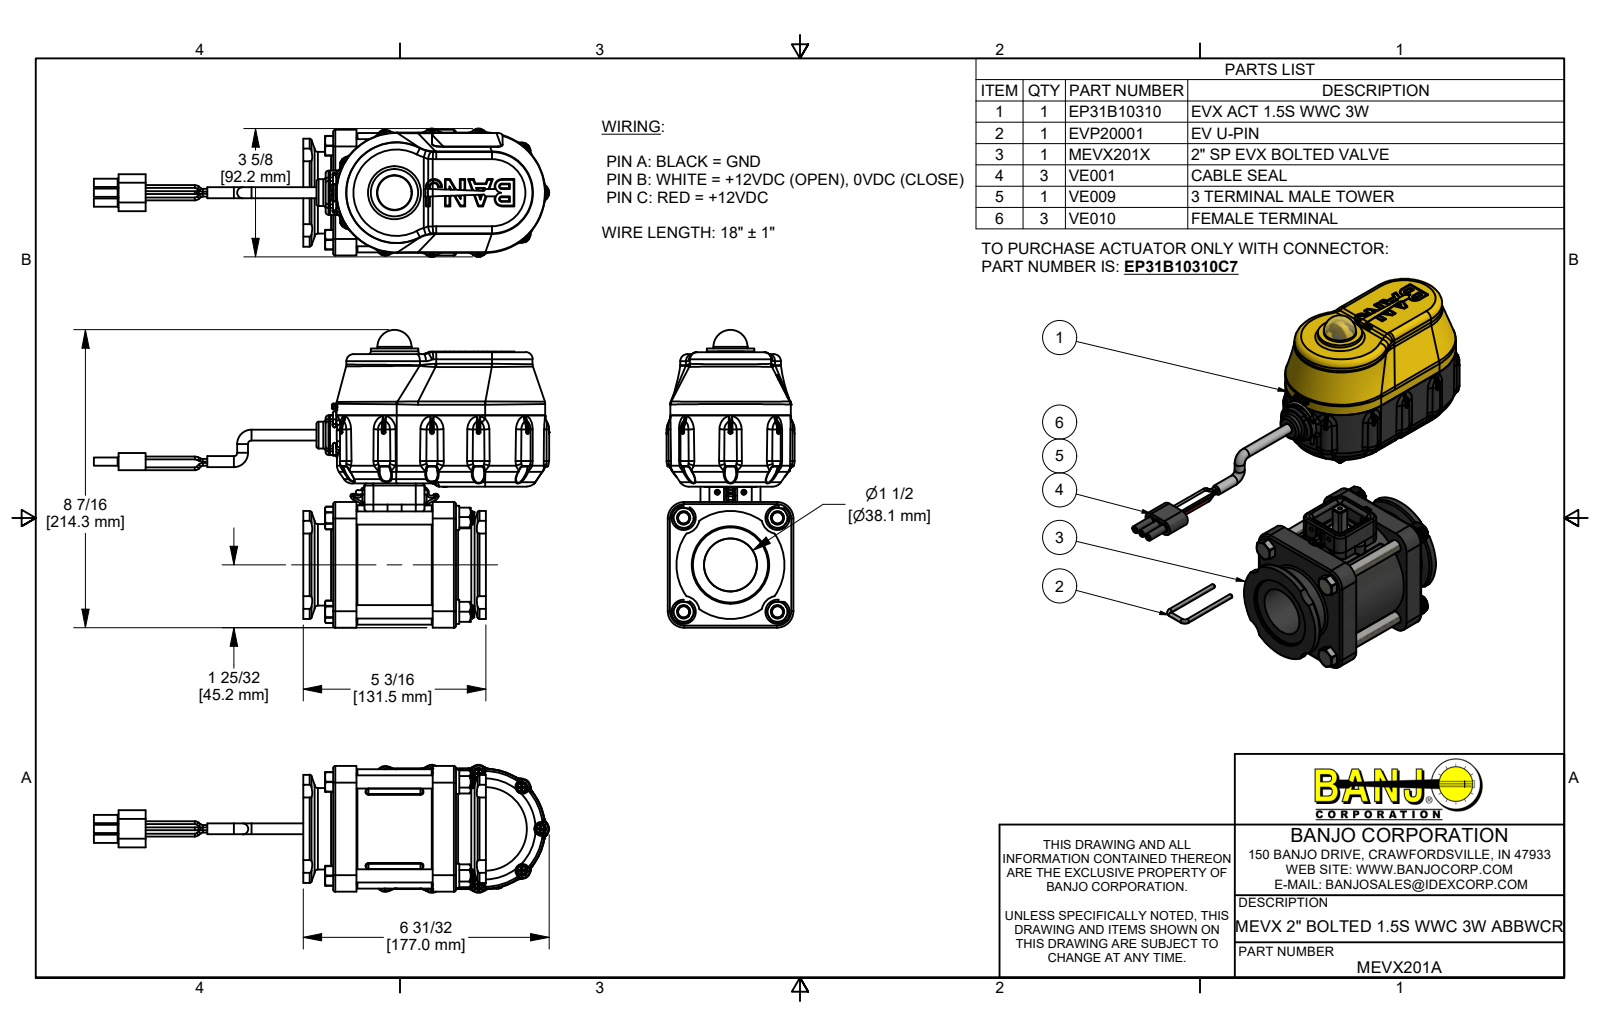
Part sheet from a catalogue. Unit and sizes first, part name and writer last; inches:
Units: inches
Overall size (bounding box): 12.901 × 8.437 × 3.63
Round holes (diameter × count): ⌀0.095 ×11, ⌀0.15 ×11, ⌀0.08 ×7, ⌀0.107 ×4, ⌀0.126 ×4, ⌀0.136 ×4, ⌀0.148 ×4, ⌀0.15 ×4, ⌀0.17 ×4, ⌀0.307 ×4, ⌀0.385 ×4, ⌀0.406 ×4
Round bosses / shafts (diameter × count): ⌀0.324 ×60, ⌀0.25 ×17, ⌀0.08 ×15, ⌀0.14 ×11, ⌀0.108 ×11, ⌀0.085 ×11, ⌀0.058 ×6, ⌀0.375 ×5
Partial cylindrical surfaces — rounded edges, fillets, slot ends (radius × count): R0.013 ×180, R0.04 ×145, R0.01 ×84, R0.02 ×78, R0.005 ×53, R0.06 ×36, R0.03 ×30, R0.08 ×28
Main face-to-face distances: 0.1, 1.685, 2.565, 0.06, 0.66, 2.818, 0.835, 2.643, 0.175, 1.983
Hole centre spacings: 1.88, 2.659, 2.69, 2.715, 0.874, 0.946, 1.662, 1.774
Volume: 65.48 in³ · Surface area: 664.4 in²
Bodies: 103 solids, 11191 faces (2863 planar, 3365 cylindrical, 4963 other)
Part name (STEP PRODUCT): MEVX201A; EP31B10310; B61905PPHS; B632038PM (+8 more)
STEP written by: Autodesk Inventor 2019 (AUTOMOTIVE_DESIGN)
